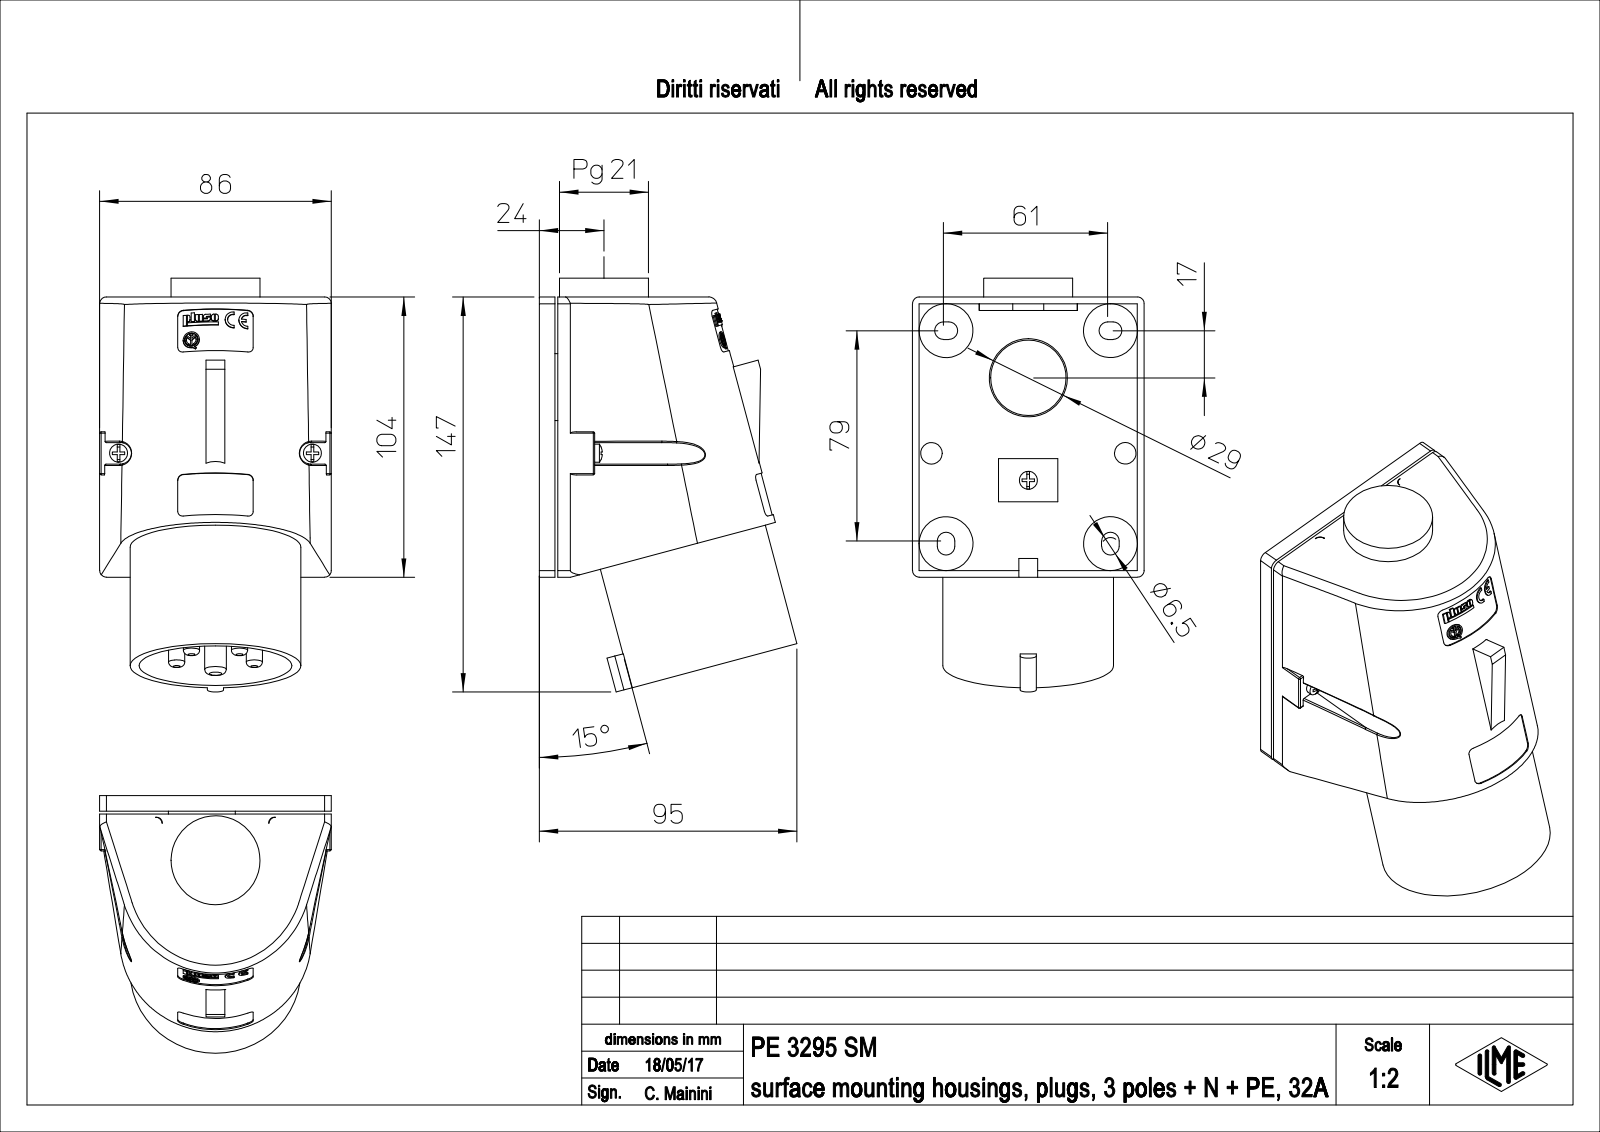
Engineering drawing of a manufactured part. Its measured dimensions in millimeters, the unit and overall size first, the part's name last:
Units: millimetres
Overall size (bounding box): 153.55 × 95.62 × 86
Round holes (diameter × count): ⌀6.1 ×4, ⌀2.8 ×2, ⌀3.2 ×2, ⌀4 ×2, ⌀4.5 ×2, ⌀4.2 ×1, ⌀5.04 ×1, ⌀27.54 ×1, ⌀29 ×1, ⌀32 ×1, ⌀56.7 ×1
Round bosses / shafts (diameter × count): ⌀6.7 ×5, ⌀6 ×5, ⌀20 ×4, ⌀8 ×3, ⌀3 ×2, ⌀63.4 ×1, ⌀33 ×1, ⌀24.84 ×1
Partial cylindrical surfaces — rounded edges, fillets, slot ends (radius × count): R0.5 ×20, R0.17 ×11, R2 ×10, R0.86 ×9, R3.25 ×8, R2.5 ×6, R0.75 ×4, R4.5 ×4
Main face-to-face distances: 1.07, 4.75, 5.82, 7, 1, 5.75, 6.82, 2.25, 2.5, 8
Hole centre spacings: 15.15, 72, 17.81, 21.93, 24.8, 28.81, 37.36, 37.37
Volume: 518 948 mm³ · Surface area: 96 274 mm²
Bodies: 1 solid, 1055 faces (668 planar, 220 cylindrical, 167 other)
Part name (STEP PRODUCT): PE_3295_SM
STEP written by: PTC Creo Elements/Direct Modeling 19.0E 27-Jun-2016 (C) Parametric Technology GmbH (AUTOMOTIVE_DESIGN)
